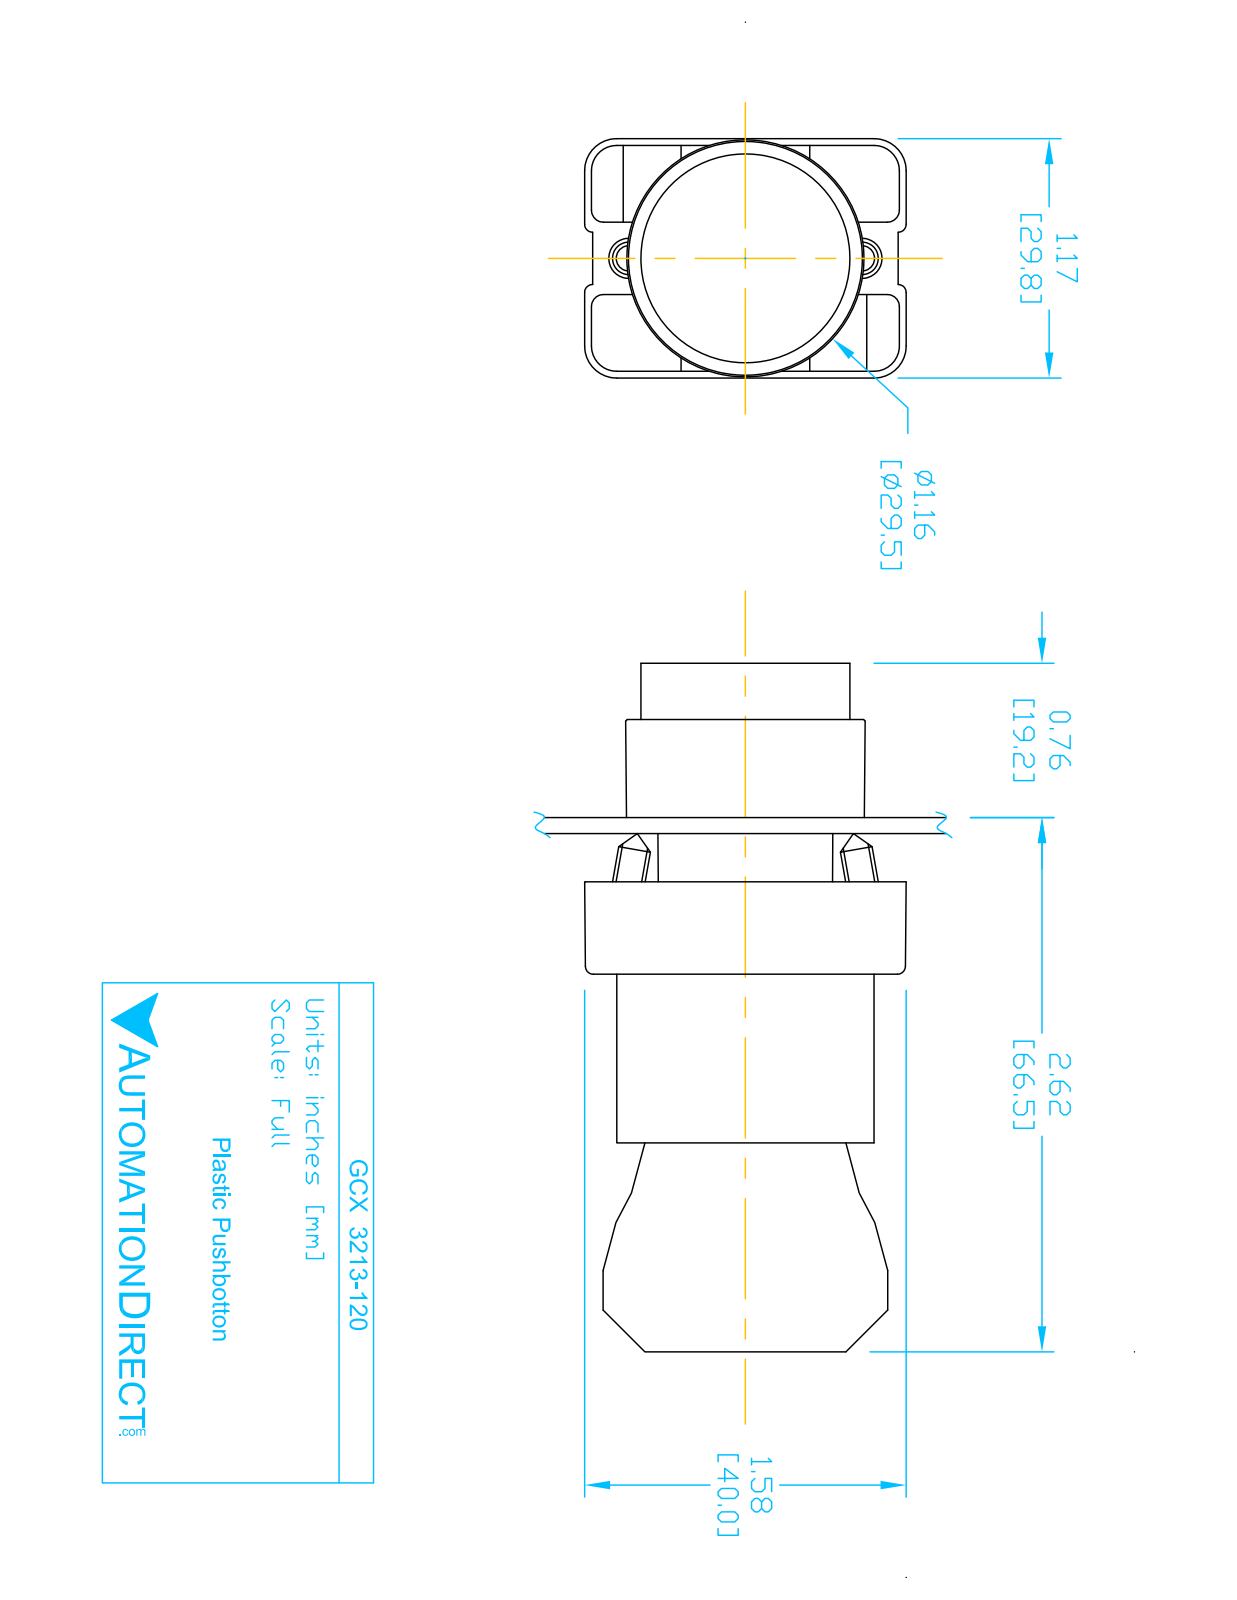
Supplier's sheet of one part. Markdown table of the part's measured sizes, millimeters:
| quantity | value |
| --- | --- |
| part name | ecx1040; GCX3213 OPERATOR; ECX1050; ECX3029-2 (+1 more) |
| STEP written by | SolidWorks 2016 (AUTOMOTIVE_DESIGN) |
| units | millimeters |
| bodies | 7 solids, 425 faces (250 planar, 144 cylindrical, 31 other) |
| overall size | 84.3 × 40.2 × 29.9 |
| volume | 44 590 mm³ |
| surface area | 23 430 mm² |
| round holes (diameter × count) | 2 × 2, 3.1 × 2, 3.3 × 2, 2.2 × 1, 5 × 1, 11.9 × 1, 22.3 × 1, 22.6 × 1, 26 × 1 |
| round bosses / shafts (diameter × count) | 4 × 4, 29.8 × 1, 25.5 × 1, 24 × 1, 21.7 × 1, 19.8 × 1, 12.8 × 1 |
| partial cylindrical surfaces (radius × count) | 1.5 × 24, 1 × 12, 3.1 × 12, 4 × 12, 1 × 8, 3.3 × 2, 0.5 × 1, 1.6 × 1 |
| main face-to-face distances | 21, 14.7, 29.7, 51.3, 30.3, 0.8, 0.8, 14.6, 29.6, 15.1 |
| hole center spacings | 6, 13.8, 12, 12.4 |
